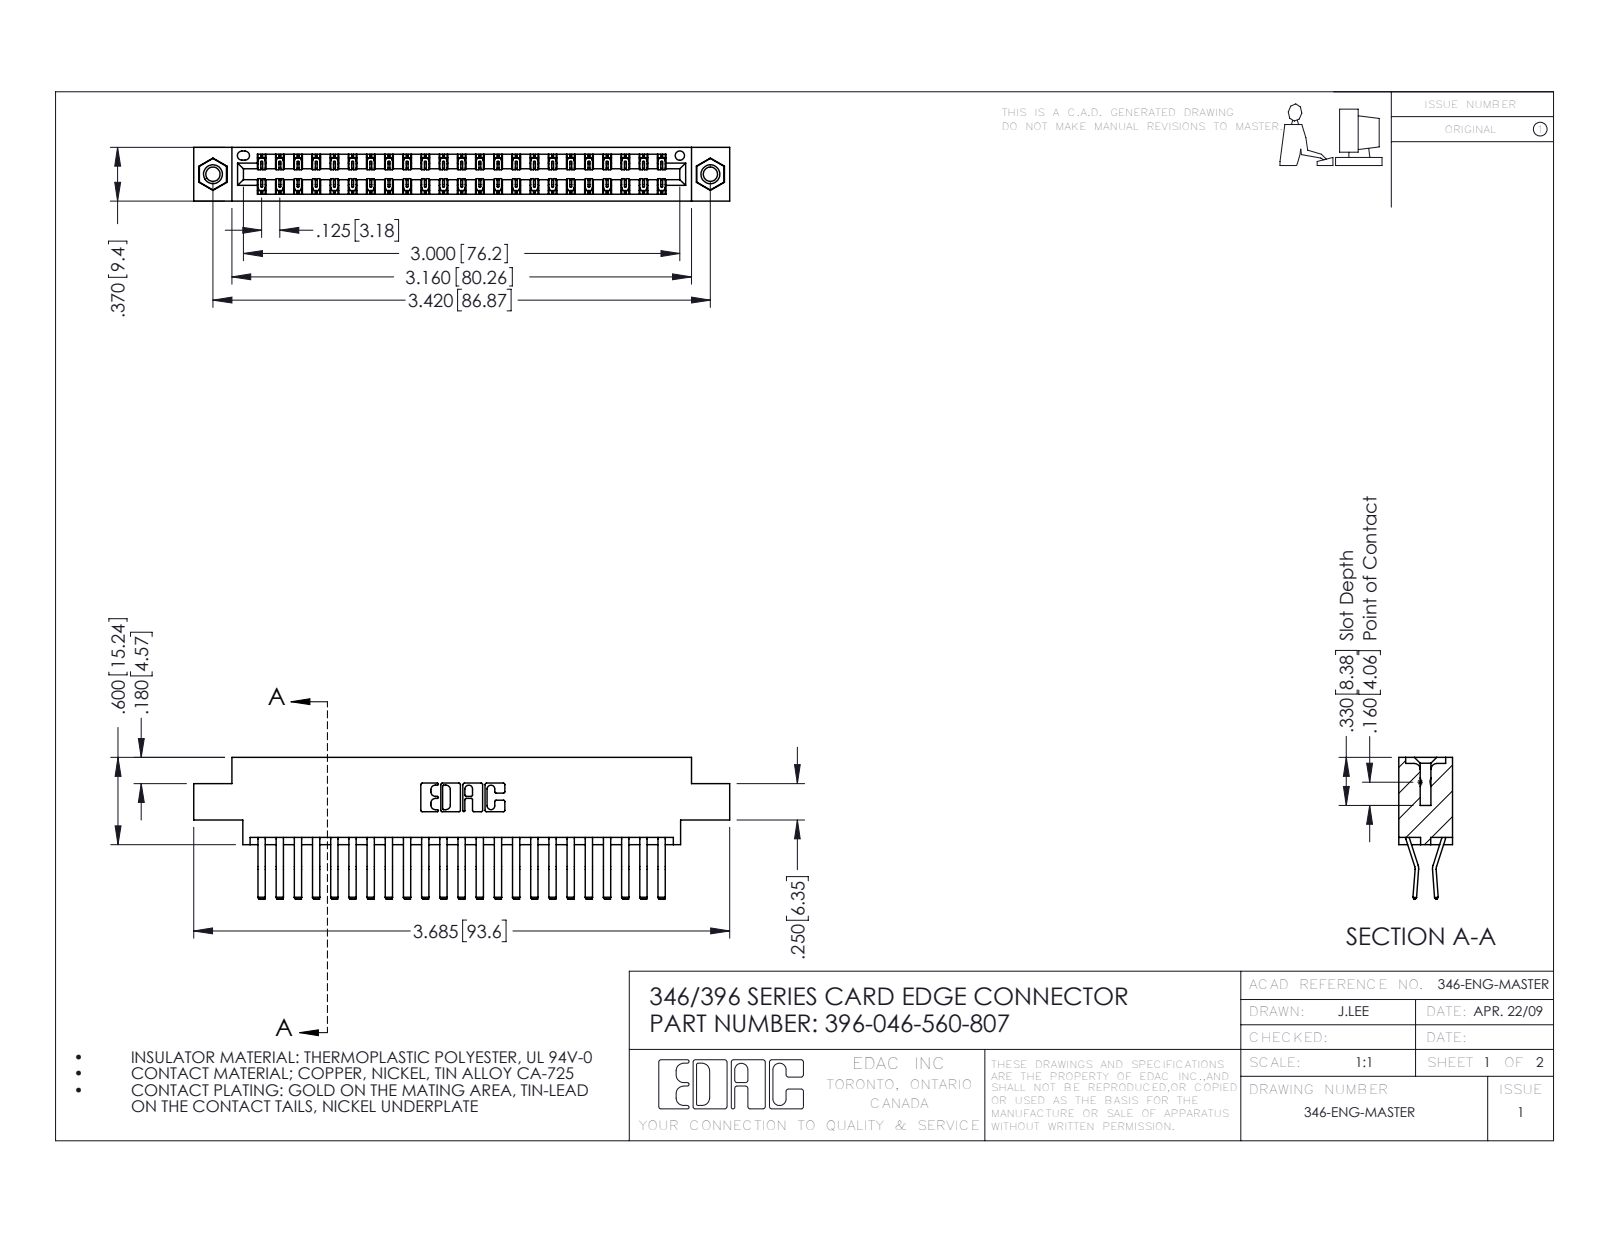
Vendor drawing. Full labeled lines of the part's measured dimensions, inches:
Part name (STEP PRODUCT): 396-046-560-807; 346 Part_0.170 Offset - 0.156 Dia-TI; 345-292-001_560 Tail; 345-250-001_345-250-005-103
STEP written by: SolidWorks 2016 (CONFIG_CONTROL_DESIGN)
Units: inches
Bodies: 49 solids, 2670 faces (1722 planar, 932 cylindrical, 16 other)
Overall size (bounding box): 3.685 × 0.975 × 0.37
Volume: 0.556 in³ · Surface area: 20.53 in²
Round holes (diameter × count): ⌀0.098 ×2, ⌀0.125 ×2, ⌀0.156 ×2, ⌀0.064 ×1
Round bosses / shafts (diameter × count): ⌀0.155 ×2
Partial cylindrical surfaces — rounded edges, fillets, slot ends (radius × count): R0.006 ×69, R0.01 ×22, R0.007 ×6, R0.031 ×6, R0.026 ×3, R0.01 ×2, R0.014 ×2, R0.022 ×2
Main face-to-face distances: 0.048, 0.322, 0.37, 0.25, 0.025, 0.072, 0.298, 0.275, 0.222, 0.148
Hole centre spacings: 0.246, 3.212, 3.42
